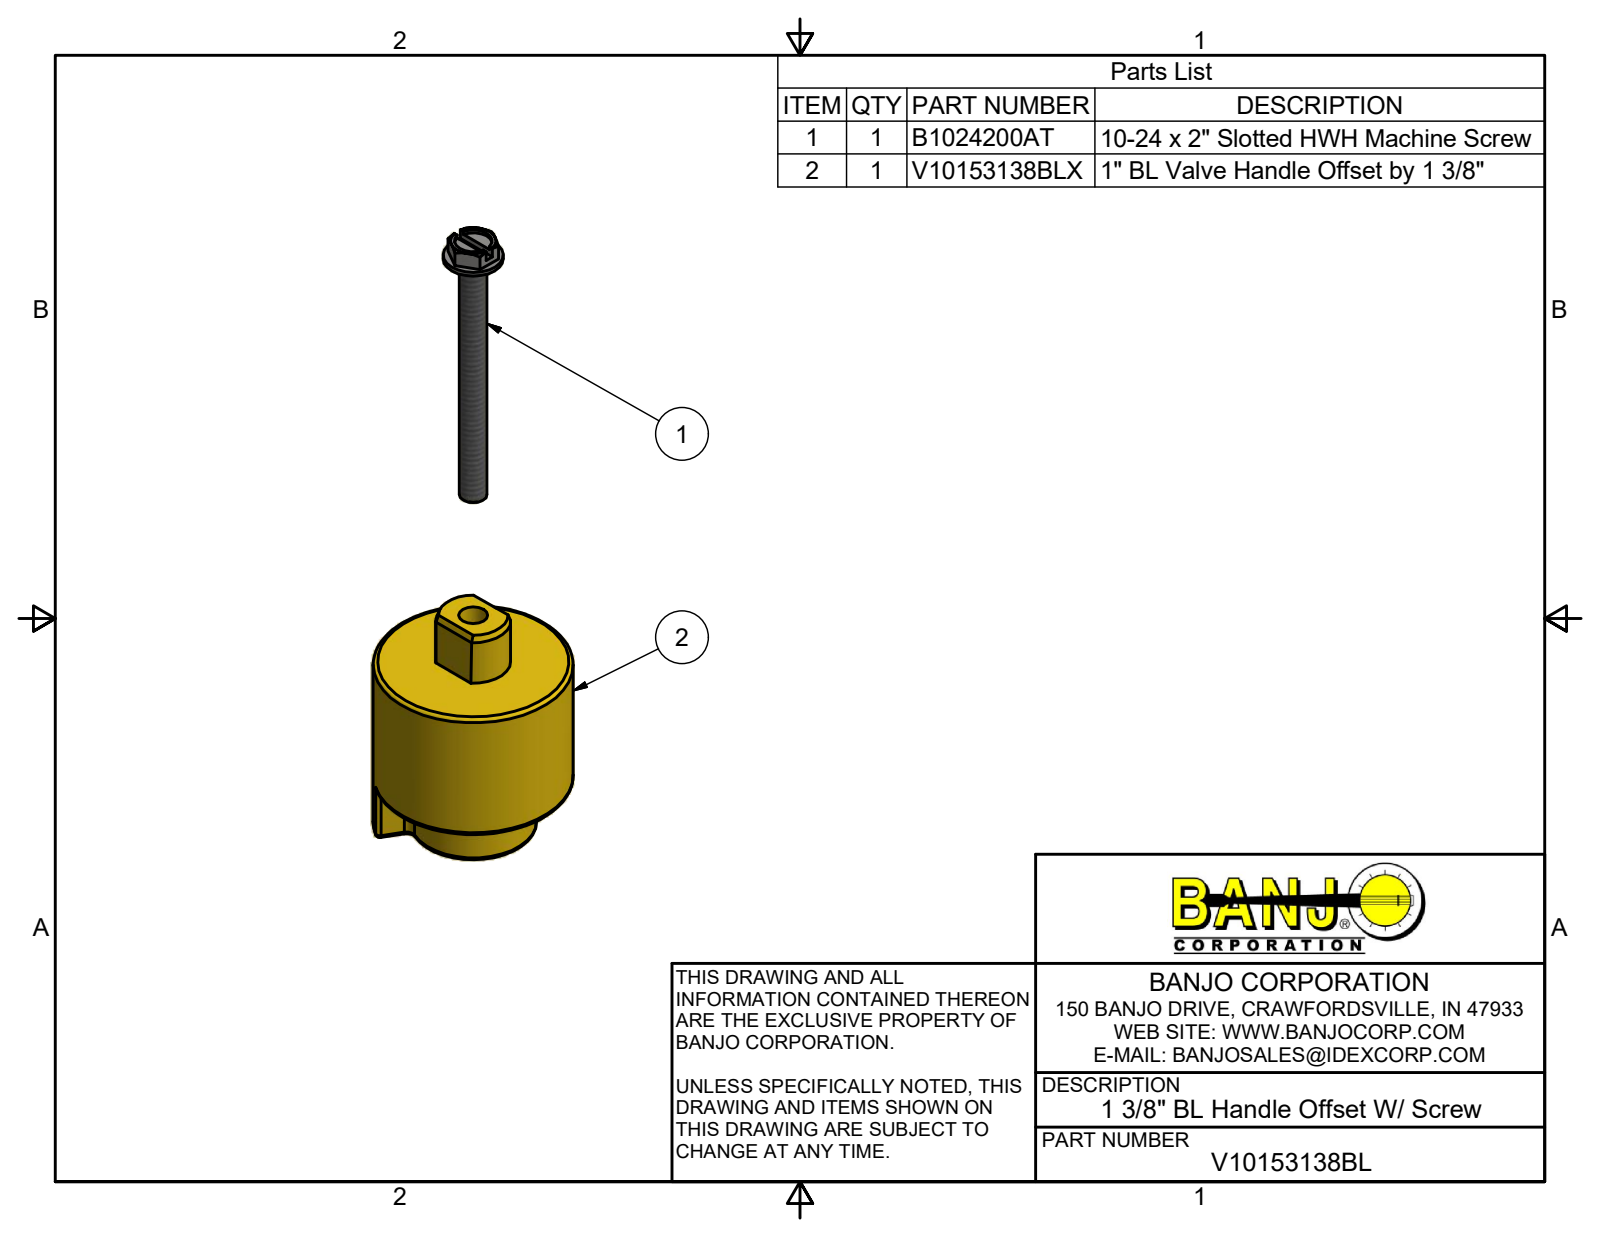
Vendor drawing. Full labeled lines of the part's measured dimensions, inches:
Part name (STEP PRODUCT): V10153138BL; V10153138BLX; B1024200AT
STEP written by: Autodesk Inventor 2017 (AUTOMOTIVE_DESIGN)
Units: inches
Bodies: 2 solids, 92 faces (37 planar, 31 cylindrical, 24 other)
Overall size (bounding box): 4.916 × 1.375 × 1.375
Volume: 1.545 in³ · Surface area: 16.74 in²
Round holes (diameter × count): ⌀0.2 ×1, ⌀0.26 ×1
Round bosses / shafts (diameter × count): ⌀1.375 ×1, ⌀0.414 ×1, ⌀0.19 ×1
Partial cylindrical surfaces — rounded edges, fillets, slot ends (radius × count): R0.03 ×8, R0.058 ×4, R0.057 ×2, R0.057 ×2, R0.257 ×1, R0.435 ×1, R0.55 ×1
Main face-to-face distances: 0.985, 0.39, 1.375, 1.25, 0.86, 0.125, 0.093, 0.293, 0.385, 1.765
